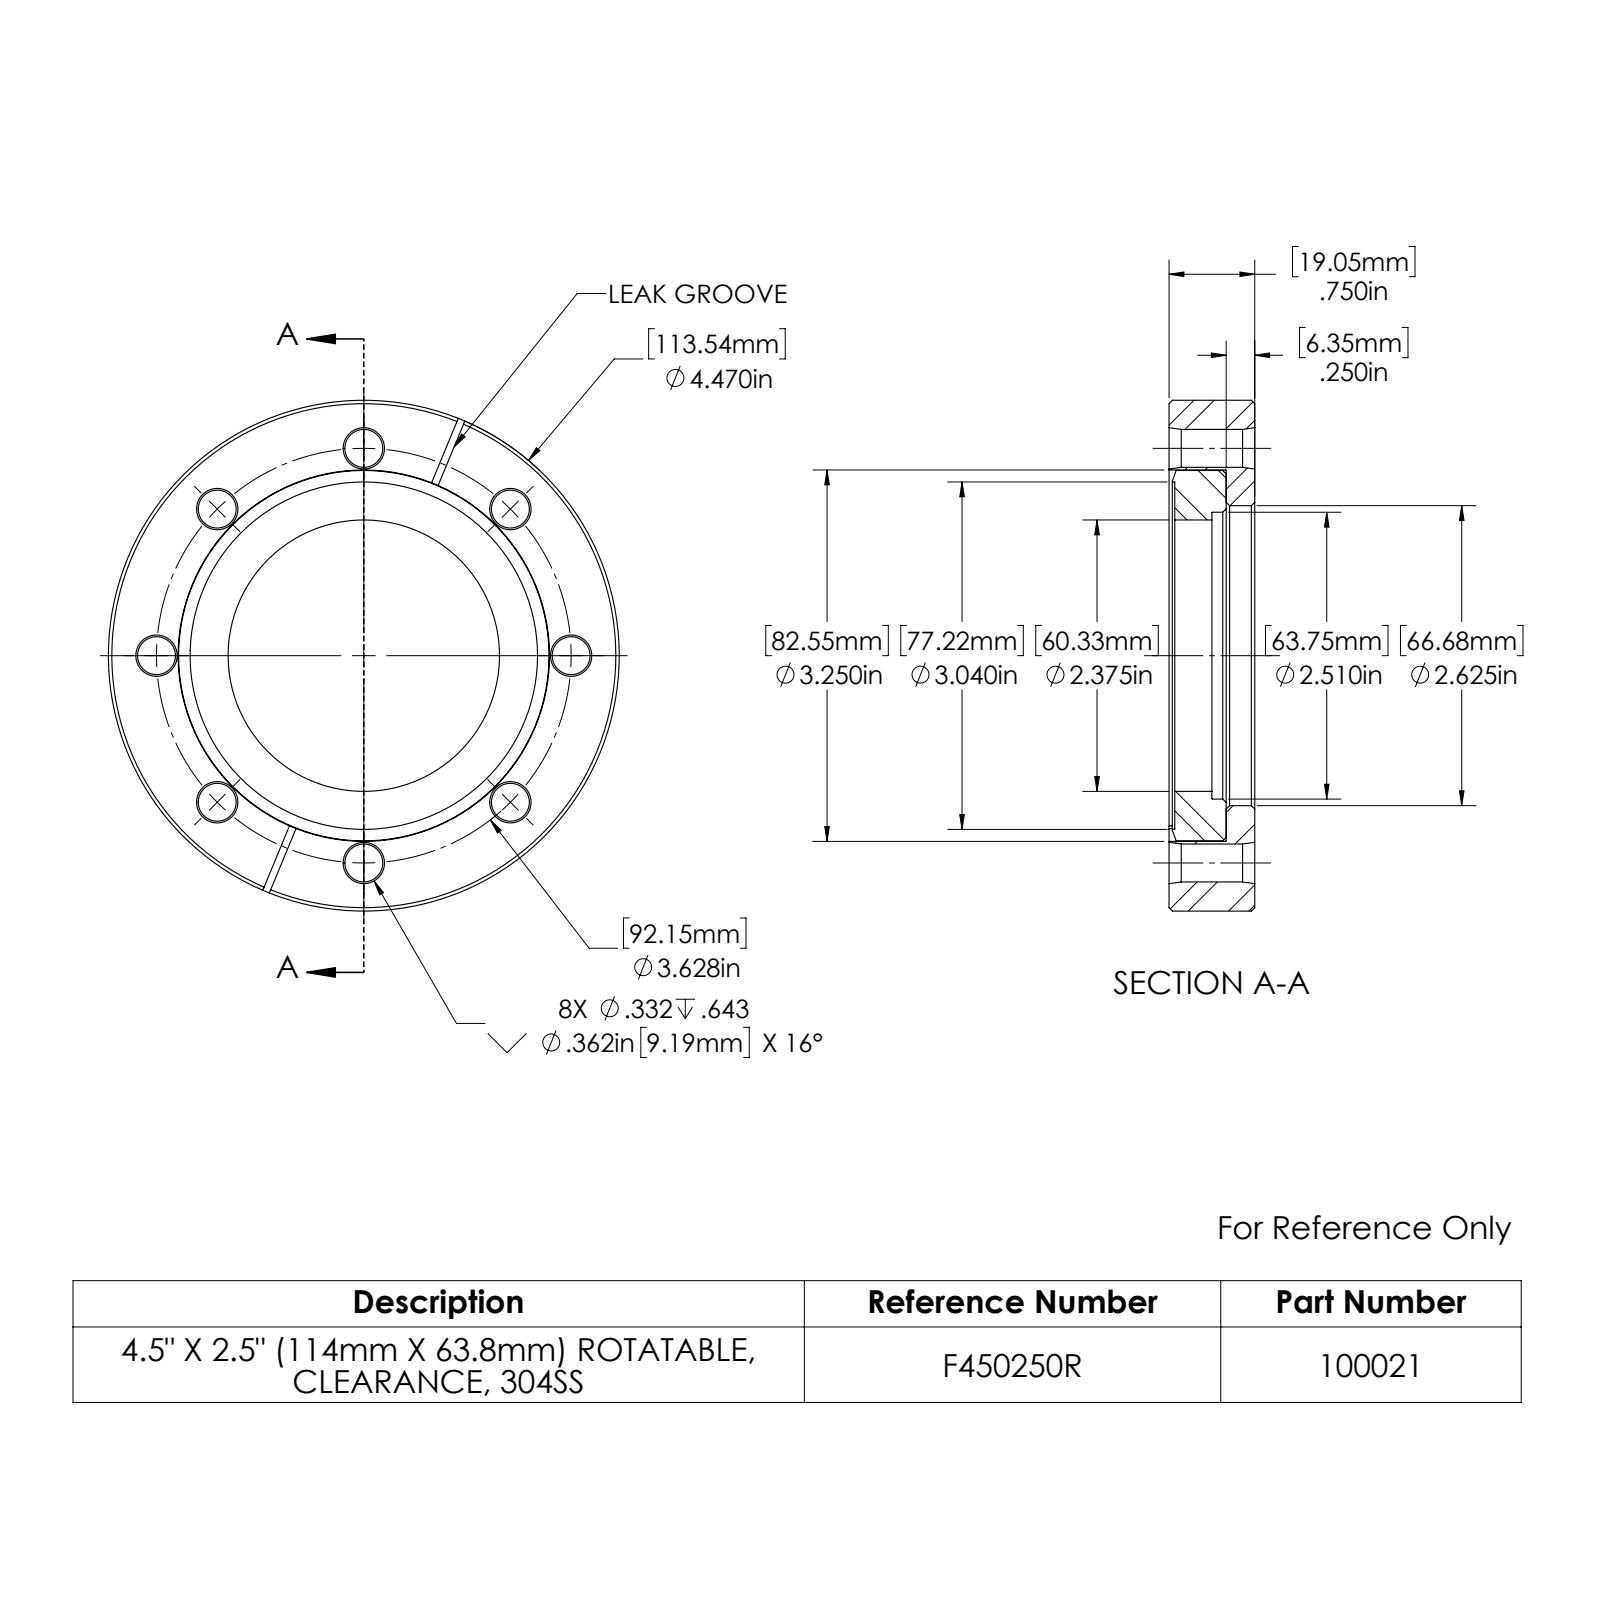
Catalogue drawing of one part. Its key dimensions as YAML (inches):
part_name: "915004; 100021; 910021"
step_written_by: "SolidWorks 2022 (AUTOMOTIVE_DESIGN)"
units: inches
bodies: {solids: 2, faces: 101, planar: 13, cylindrical: 30, other: 58}
overall_size: [4.47, 4.47, 0.75]
volume: 7.362
surface_area: 57.68
round_holes:
  - {diameter: 0.332, count: 8}
  - {diameter: 2.375, count: 1}
  - {diameter: 2.51, count: 1}
  - {diameter: 2.625, count: 1}
  - {diameter: 3.04, count: 1}
  - {diameter: 3.25, count: 1}
round_bosses_or_shafts:
  - {diameter: 4.47, count: 1}
  - {diameter: 3.241, count: 1}
face_to_face_distances: [0.75, 0.5, 0.25, 0.05, 0.45, 0.7, 0.375, 0.325, 0.125, 0.375]
hole_center_spacings: [1.814, 2.565, 1.388, 1.389, 3.352, 3.352, 3.628, 1.814]
